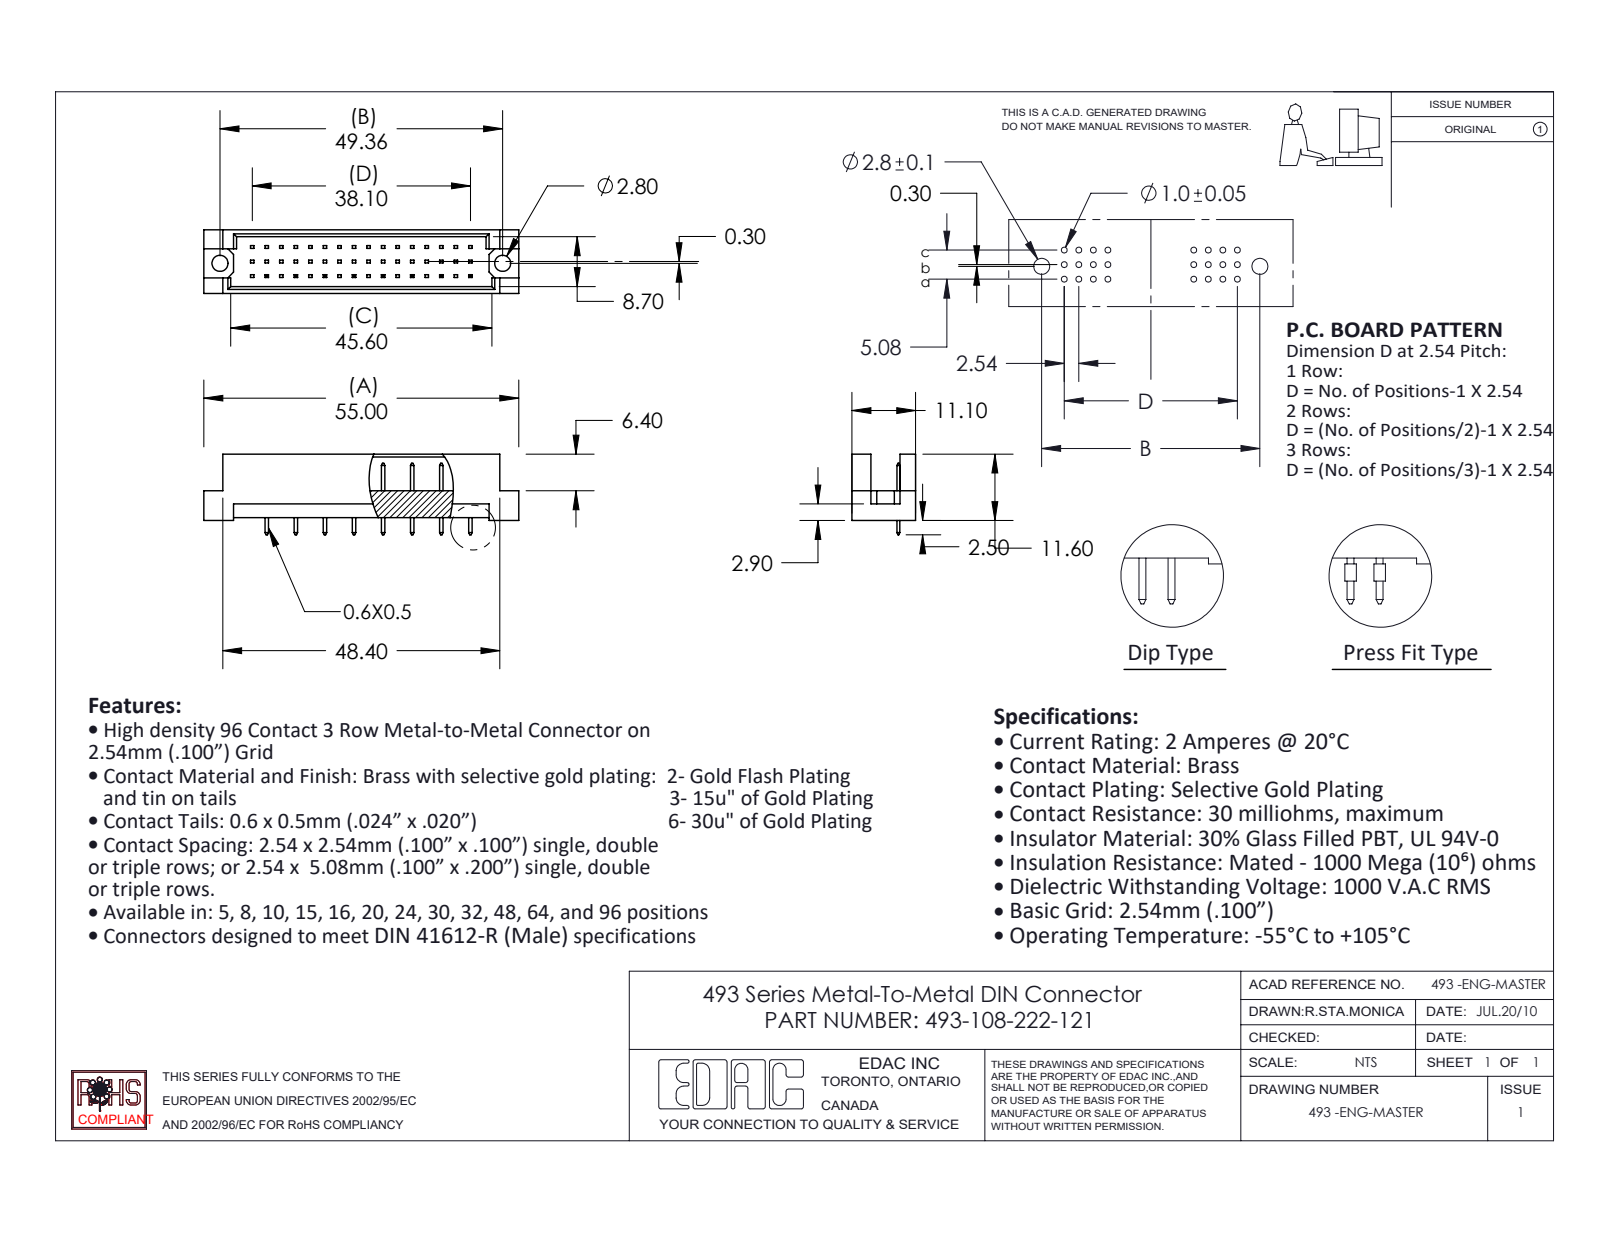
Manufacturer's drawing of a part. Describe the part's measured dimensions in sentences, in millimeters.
The part is named "493 Part_48; 493-290_22; 493-108-222-121". Its 3-D file was written by "SolidWorks 2020 (CONFIG_CONTROL_DESIGN)". It is 9 solids with 356 faces: 352 planar, 4 cylindrical and 0 other. Overall it measures 55 by 14.1 by 11.1 millimeters. Its volume is 3 302 cubic millimeters and its surface area 3 973 square millimeters. Round holes: 2 of diameter 2.8. The main face-to-face distances are 1.2, 9.9, 11.1, 8.7, 4.7, 0.5, 5.08, 2.54, 2.76, 8.34. The hole center spacings are 49.36.
